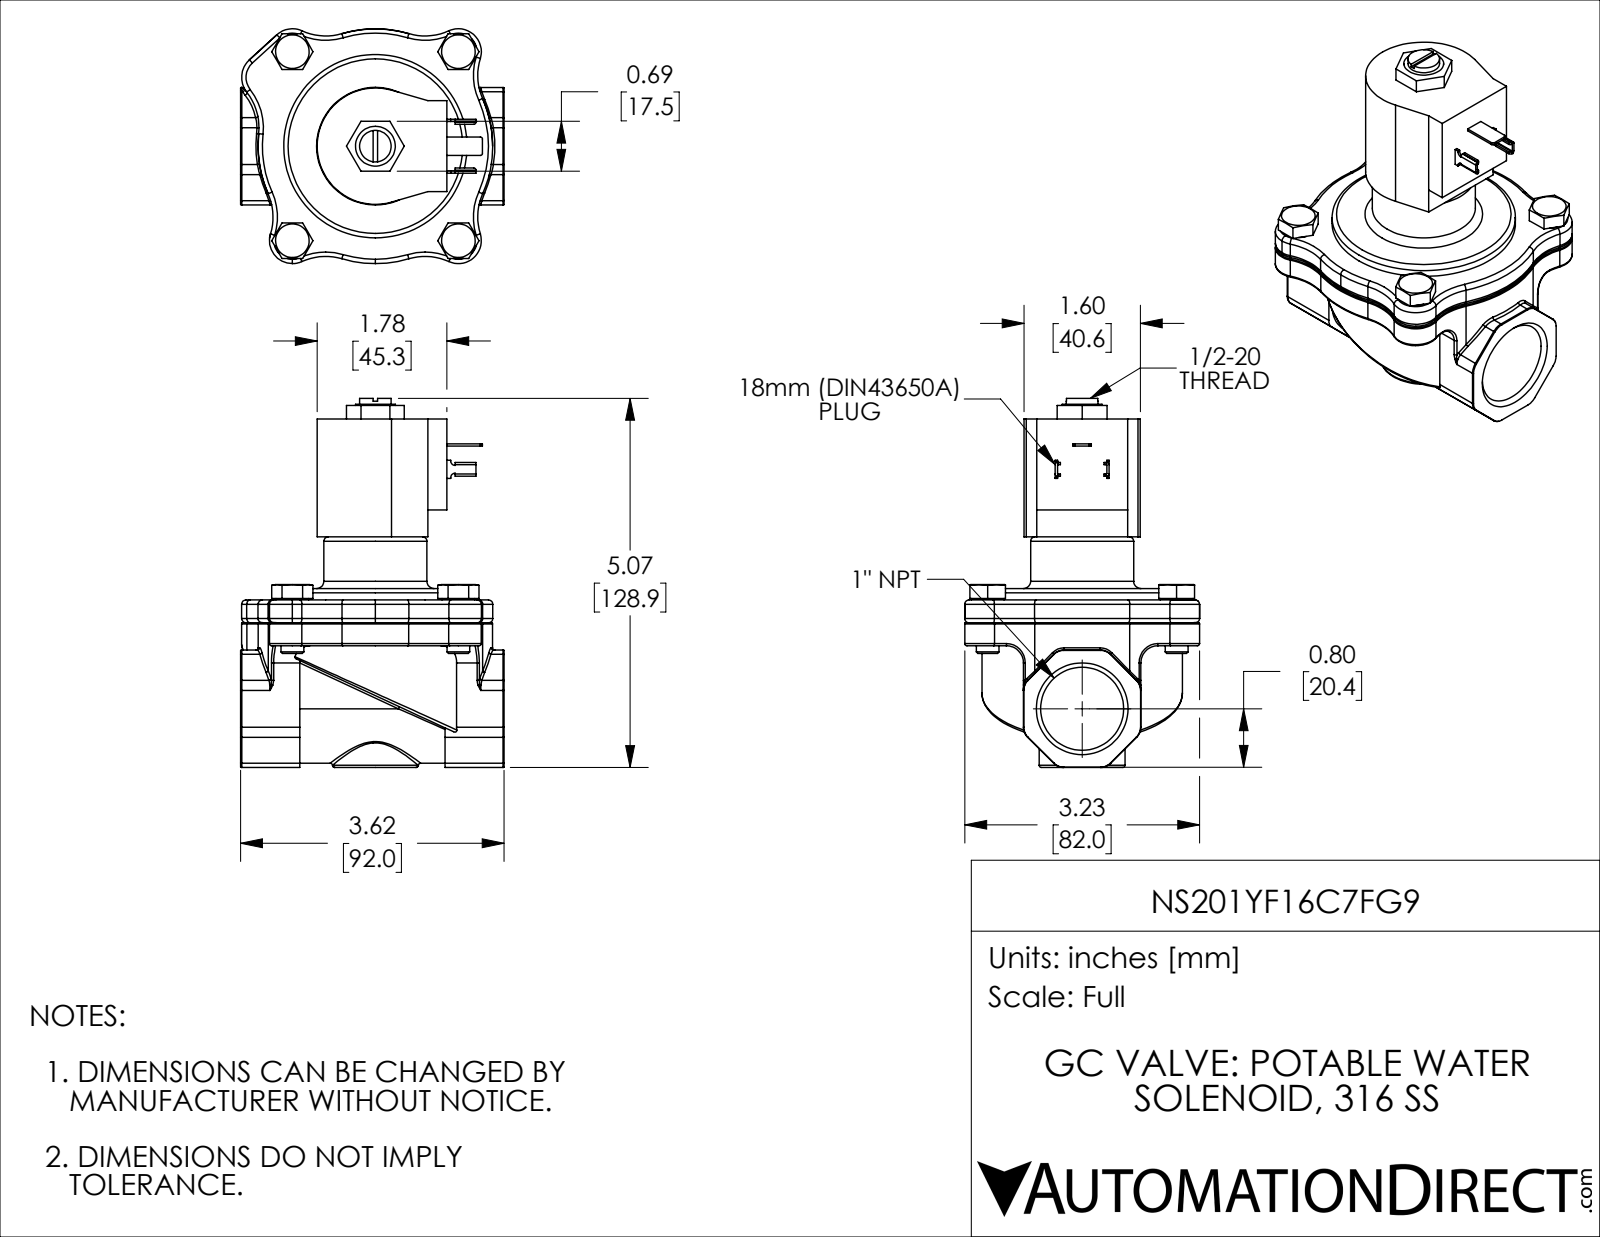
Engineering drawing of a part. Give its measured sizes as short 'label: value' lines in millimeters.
name: NS201YF16C7FG9
written by: SolidWorks 2018 (AUTOMOTIVE_DESIGN)
unit: mm
bodies: 12 solids, 603 faces (162 planar, 221 cylindrical, 220 other)
size: 128.9 × 92 × 82
volume: 306 300 mm³; area: 66 060 mm²
holes: 4× ⌀6.4, 4× ⌀8, 1× ⌀3.2, 1× ⌀6, 1× ⌀12.4, 1× ⌀12.8, 1× ⌀24.1, 1× ⌀29, 1× ⌀76.2
bosses: 4× ⌀11.4, 4× ⌀8, 1× ⌀67.3, 1× ⌀64, 1× ⌀36, 1× ⌀30, 1× ⌀13.9, 1× ⌀11
rounds: 26× R0.8, 16× R20, 8× R0.8, 8× R5, 6× R8, 2× R1.5, 2× R6, 1× R8.3
face distances: 8, 0.8, 8.8, 71.9, 71.1, 63.1, 4, 30.8, 30, 22
hole spacings: 66, 43.9, 58, 87.8, 43.9, 43.9, 57.8, 58
